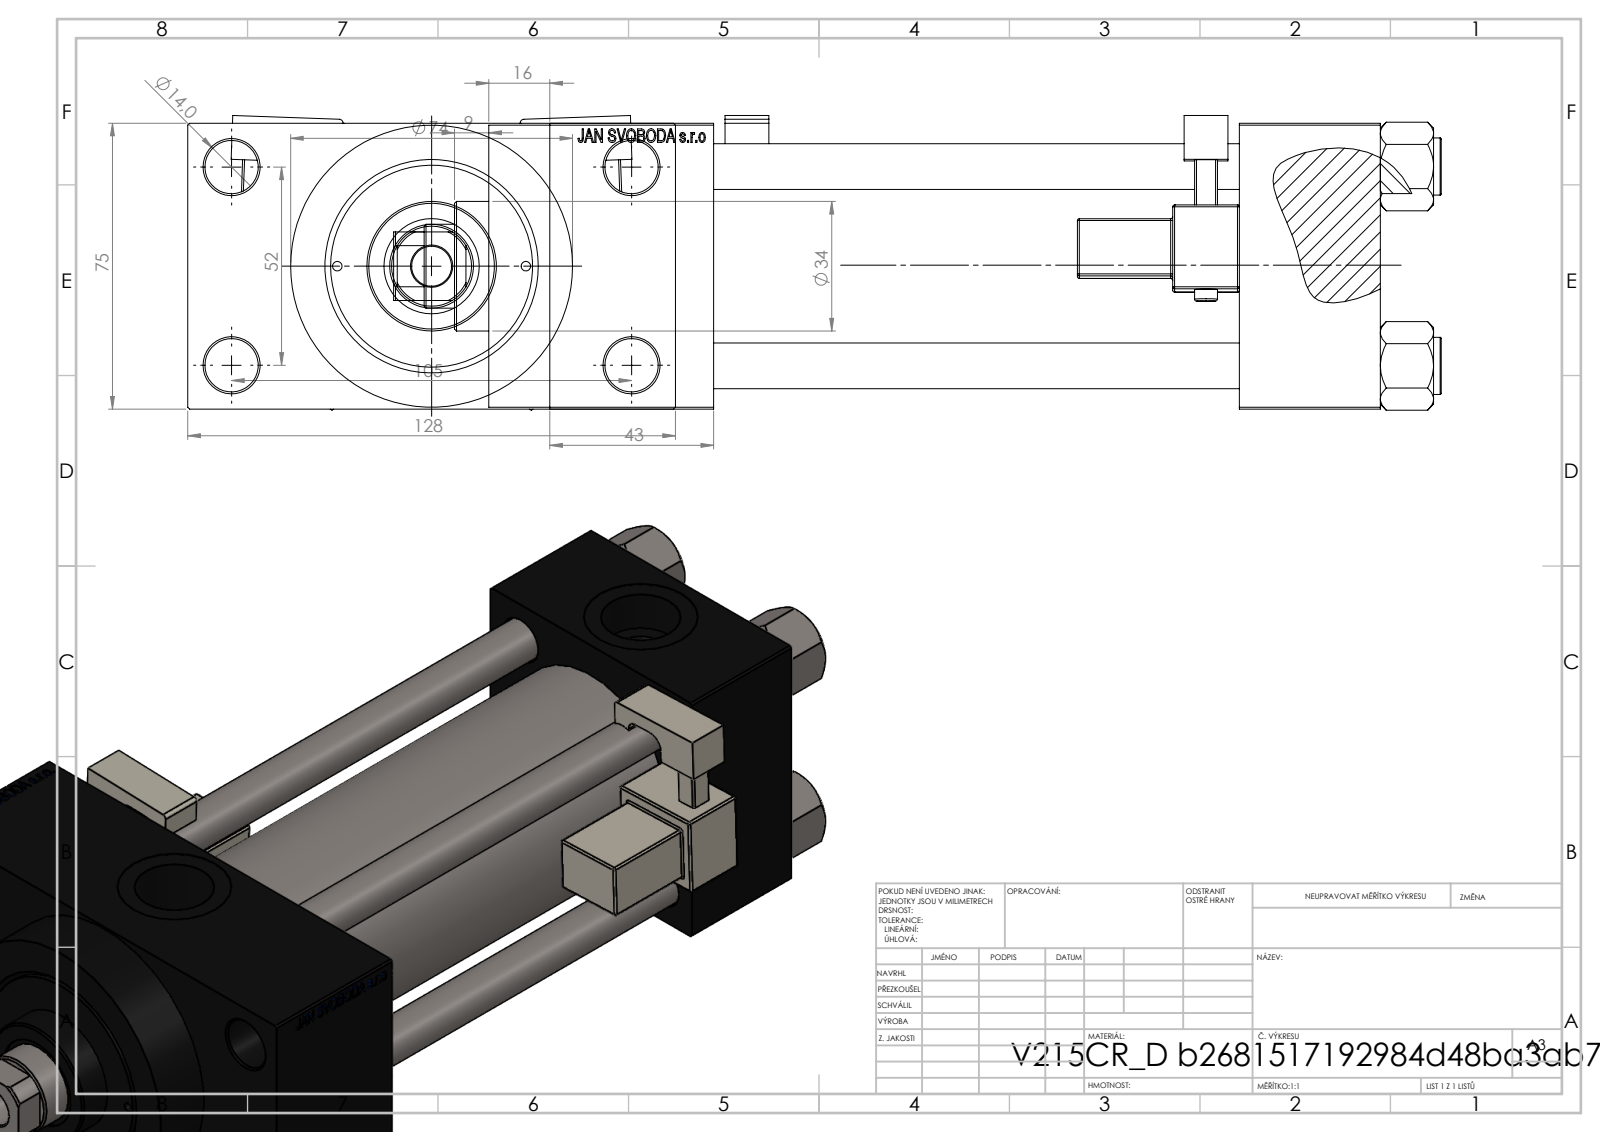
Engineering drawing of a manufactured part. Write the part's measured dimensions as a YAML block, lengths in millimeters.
part_name: "NUT_M5_D; V215CR_D_Body; V215_VC_A; V215CR_D_TYCINKA (+2 more)"
step_written_by: "SolidWorks 2019 (CONFIG_CONTROL_DESIGN)"
units: millimeters
bodies: {solids: 13, faces: 1266, planar: 557, cylindrical: 153, other: 556}
overall_size: [275, 128, 77.3]
volume: 954009
surface_area: 221385
round_holes:
  - {diameter: 12, count: 4}
  - {diameter: 14, count: 4}
  - {diameter: 2.5, count: 2}
  - {diameter: 7, count: 2}
  - {diameter: 20.96, count: 2}
  - {diameter: 30, count: 2}
  - {diameter: 10.5, count: 1}
  - {diameter: 22, count: 1}
  - {diameter: 25, count: 1}
  - {diameter: 41, count: 1}
  - {diameter: 50, count: 1}
  - {diameter: 53, count: 1}
round_bosses_or_shafts:
  - {diameter: 15, count: 4}
  - {diameter: 6, count: 2}
  - {diameter: 74, count: 1}
  - {diameter: 56, count: 1}
  - {diameter: 34, count: 1}
partial_cylinders:
  - {radius: 0.5, count: 48}
  - {radius: 1, count: 2}
  - {radius: 2.5, count: 2}
  - {radius: 4, count: 2}
  - {radius: 10.5, count: 1}
face_to_face_distances: [75, 138, 101.5, 37, 175, 26.5, 218, 181, 43, 16]
hole_center_spacings: [26.19, 26.35, 36.98, 38.03, 52.3, 57.22, 58.43, 58.59]
